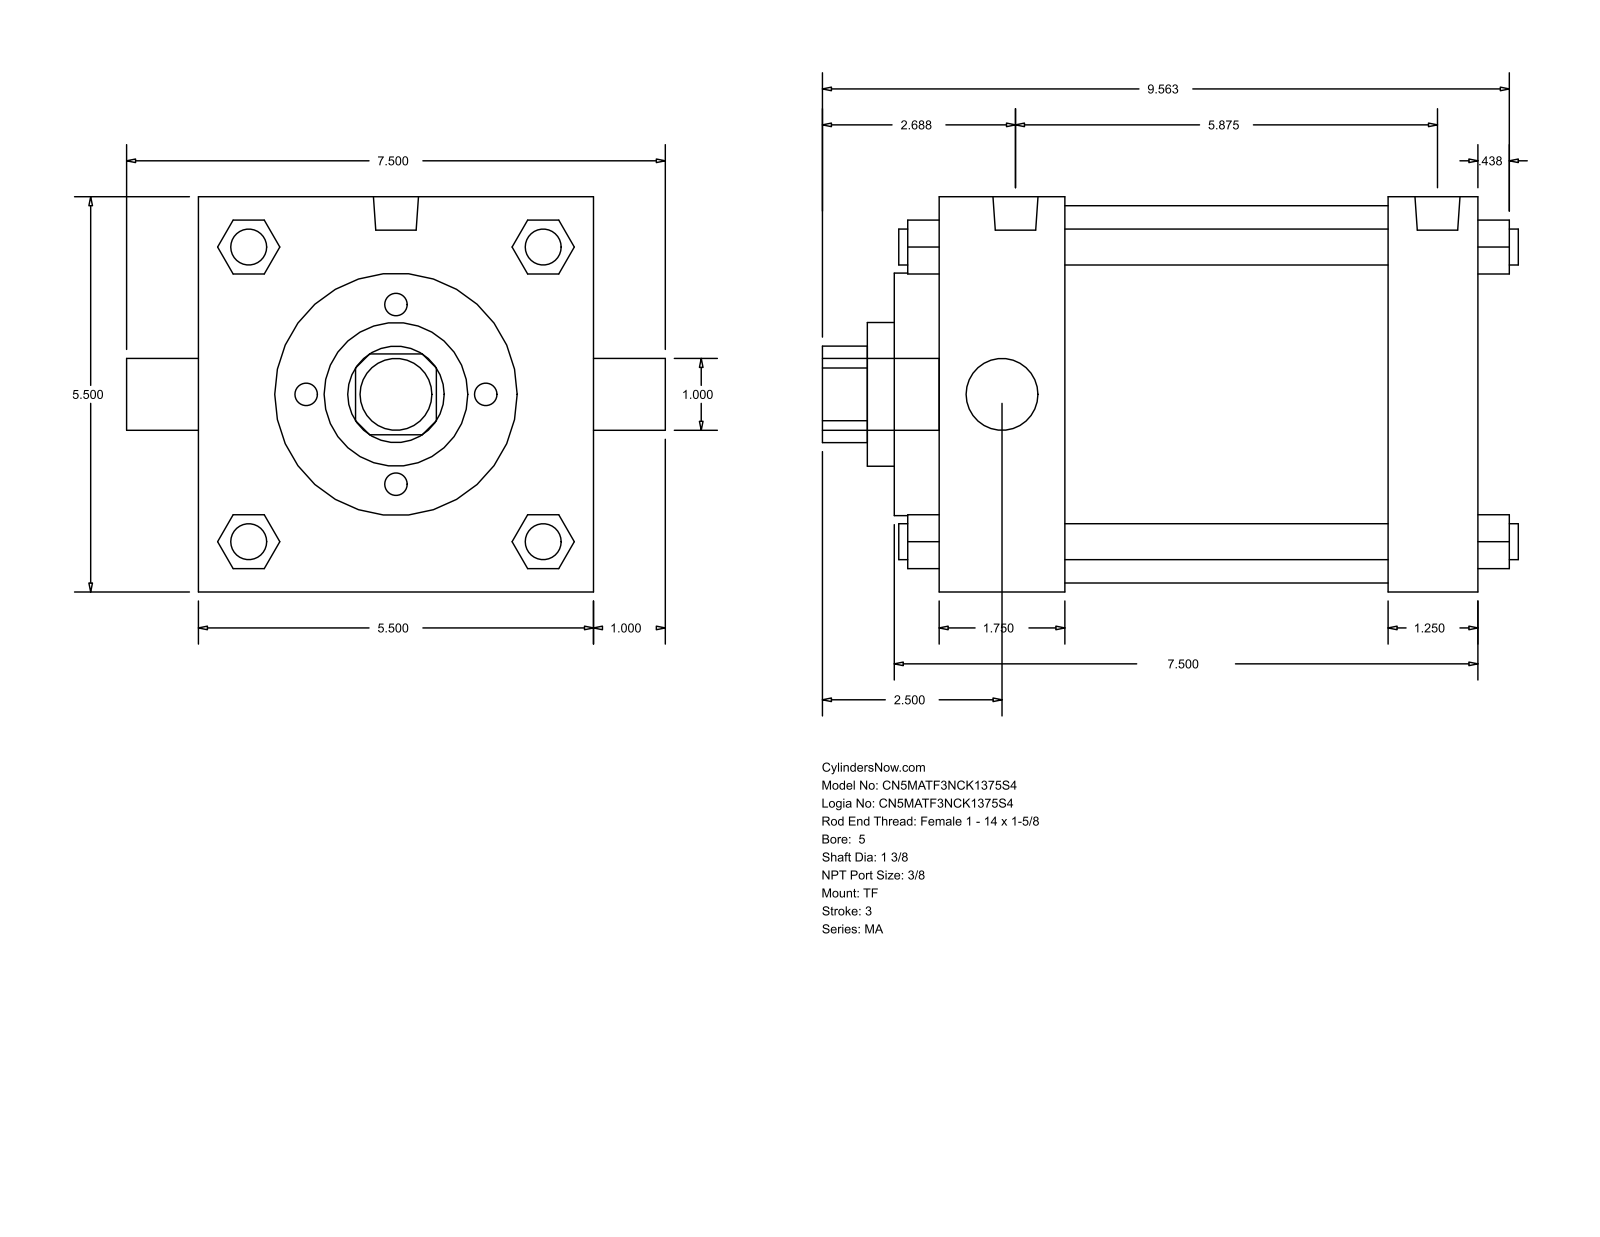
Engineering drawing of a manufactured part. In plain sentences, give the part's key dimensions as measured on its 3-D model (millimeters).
The part is named "MA_TF__0500_1.375". Its 3-D file was written by "GSSL Pune (CONFIG_CONTROL_DESIGN)". It is 0 solids with 122 faces: 93 planar, 29 cylindrical and 0 other. Overall it measures 246.06 by 190.5 by 139.7 millimeters. Round holes: 1 of diameter 25.4, 1 of diameter 34.92, 1 of diameter 50.8, 1 of diameter 85.72, 1 of diameter 133.35. Round bosses or shafts: 4 of diameter 12.7, 3 of diameter 11.11, 2 of diameter 15.93, 1 of diameter 25.4. Partial cylindrical surfaces (rounded edges, fillets, slot ends): 1 of radius 17.06. The main face-to-face distances are 139.7, 190.51, 158.76, 31.75, 44.45, 114.31, 146.06, 15.87, 60.32, 174.63.
